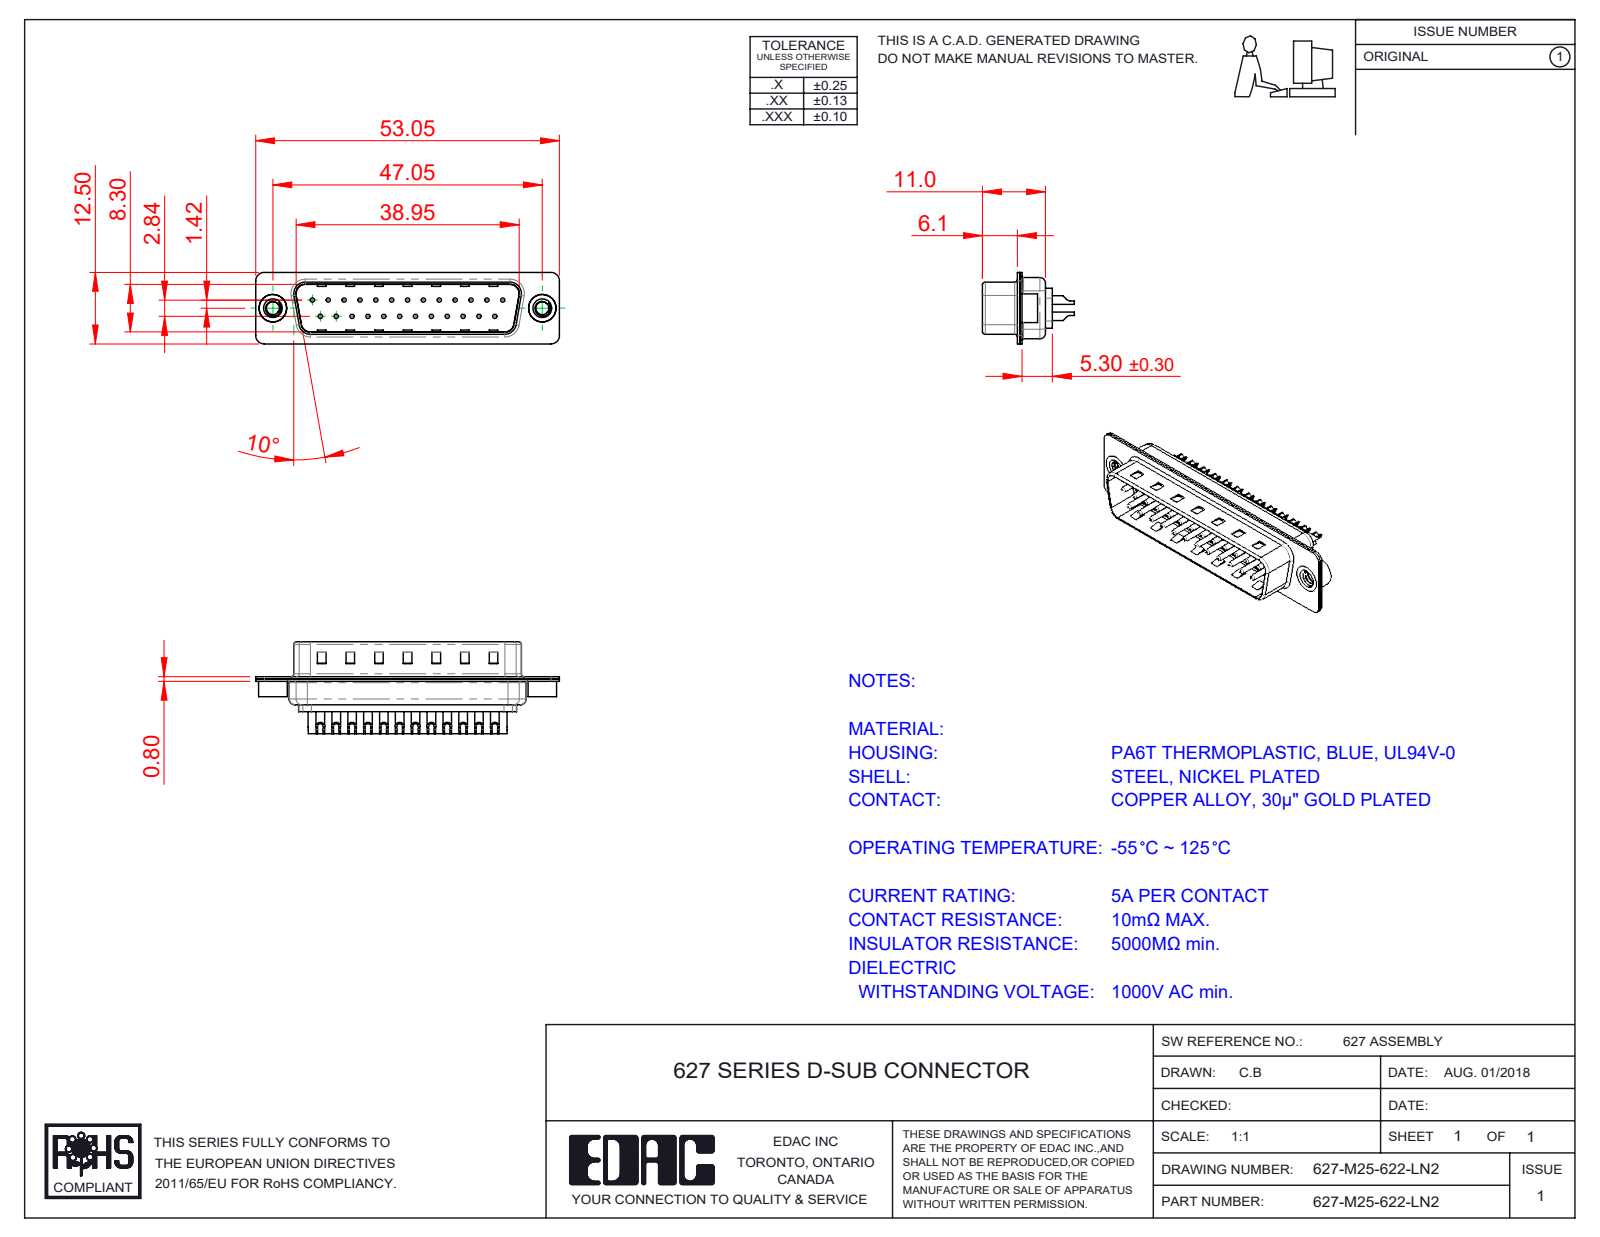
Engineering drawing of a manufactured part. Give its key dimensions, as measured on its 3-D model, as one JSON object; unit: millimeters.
{"part_name": "627M 4-40 Threaded Rivet; 627-M25-622-LN2; 627M Shell Rear_25 Contacts; 627M Housing_25 Contacts (+3 more)", "step_written_by": "SolidWorks 2020 (CONFIG_CONTROL_DESIGN)", "units": "millimeters", "bodies": {"solids": 30, "faces": 1301, "planar": 396, "cylindrical": 537, "other": 368}, "overall_size": [53.05, 16.05, 12.5], "volume_mm3": 2776, "surface_area_mm2": 7078, "round_holes": [[0.75, 25], [1, 25], [1.6, 25], [2, 25], [2.26, 2], [4, 2], [4.8, 2]], "round_bosses_or_shafts": [[1.5, 25], [5, 2], [4.9, 2]], "partial_cylinders_radius": [[1.5, 16], [2, 12], [0.5, 8], [1.6, 8], [1, 6], [0.25, 4], [0.6, 4], [0.65, 4]], "face_to_face_distances": [0.4, 0.8, 9.5, 9.1, 8.7, 9.9, 1.2, 0.75, 0.35, 6.1], "hole_center_spacings": [3.16, 2.77, 5.54, 8.31, 11.08, 13.85, 16.62, 5.03]}
